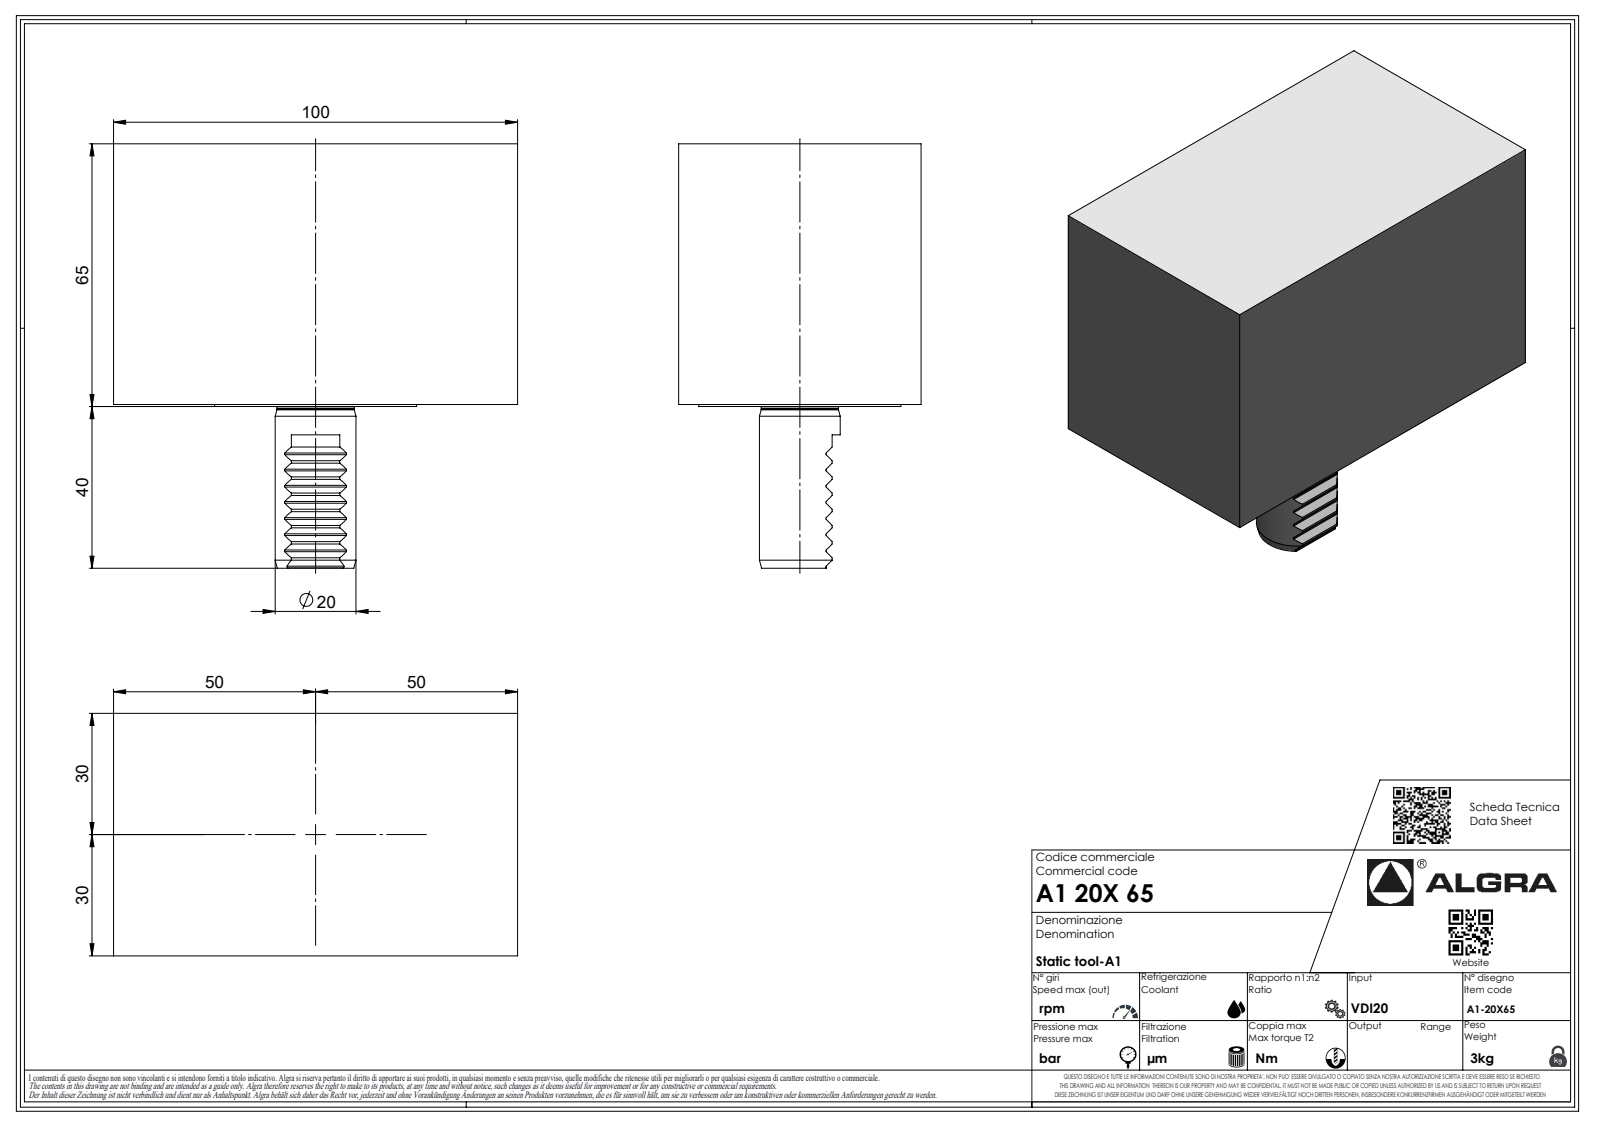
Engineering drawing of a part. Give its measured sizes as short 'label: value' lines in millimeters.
name: A120X65
written by: SolidWorks 2023 (AUTOMOTIVE_DESIGN)
unit: mm
bodies: 1 solid, 257 faces (175 planar, 38 cylindrical, 44 other)
size: 105 × 100 × 60
volume: 398 800 mm³; area: 35 705 mm²
holes: 1× ⌀2.1, 1× ⌀10
bosses: 1× ⌀50, 1× ⌀20, 1× ⌀19.1, 1× ⌀6.37, 1× ⌀1.7
rounds: 8× R0.3, 7× R0.33, 7× R0.52, 7× R3.7, 1× R0.21
face distances: 60, 64.5, 100, 0.5, 65, 2.83, 40, 40.5, 105, 5.66
